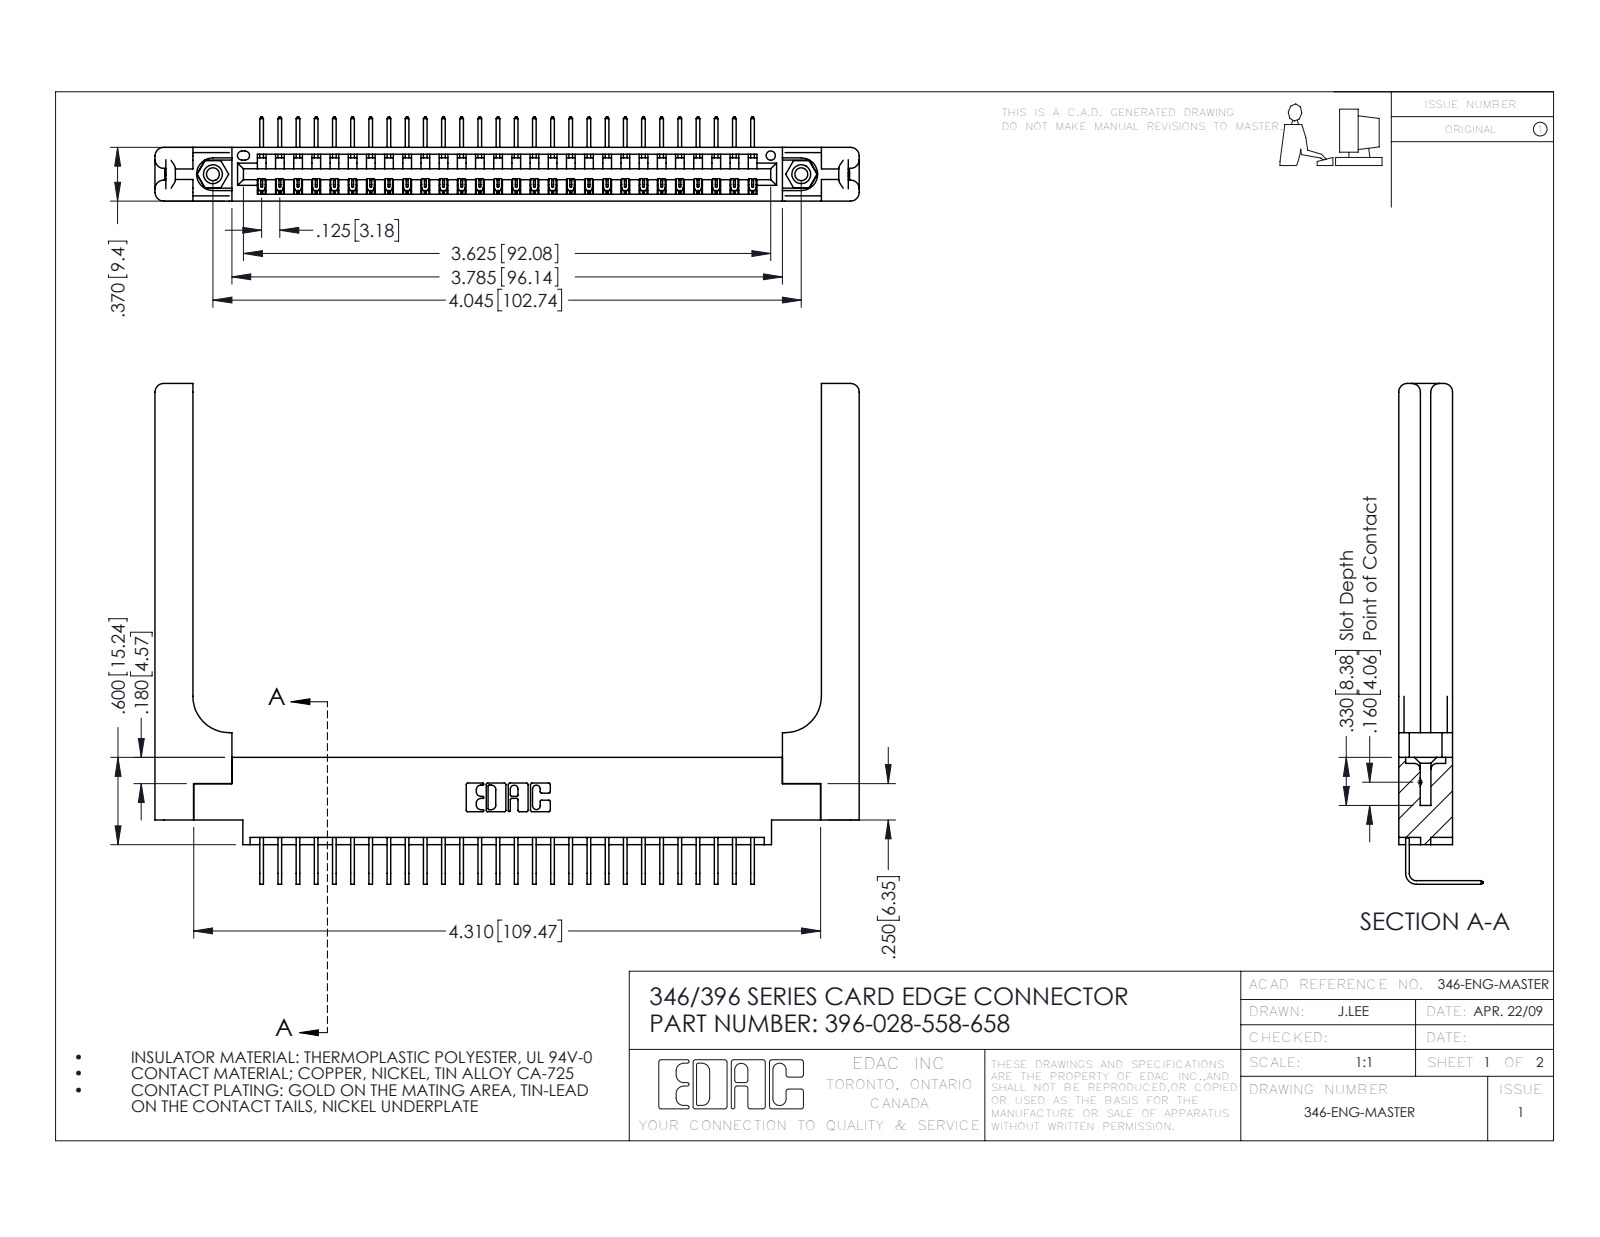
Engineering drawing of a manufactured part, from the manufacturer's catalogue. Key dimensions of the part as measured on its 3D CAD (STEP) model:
Part name (STEP PRODUCT): 345-292-001_558 Tail - 2; 345-250-001_345-250-001-102; 346-220-058_345-220-058; 396-028-558-658 (+1 more)
STEP written by: SolidWorks 2016 (CONFIG_CONTROL_DESIGN)
Units: inches
Bodies: 33 solids, 2062 faces (1404 planar, 598 cylindrical, 60 other)
Overall size (bounding box): 4.841 × 3.443 × 0.58
Volume: 1.167 in³ · Surface area: 31.39 in²
Round holes (diameter × count): ⌀0.089 ×2, ⌀0.125 ×2, ⌀0.156 ×2, ⌀0.064 ×1
Round bosses / shafts (diameter × count): ⌀0.155 ×2
Partial cylindrical surfaces — rounded edges, fillets, slot ends (radius × count): R0.006 ×56, R0.01 ×22, R0.06 ×16, R0.007 ×6, R0.031 ×6, R0.026 ×3, R0.03 ×2, R0.031 ×2
Main face-to-face distances: 0.37, 0.322, 0.072, 0.048, 0.148, 0.15, 0.025, 0.25, 0.298, 0.076
Hole centre spacings: 0.246, 3.837, 4.045
